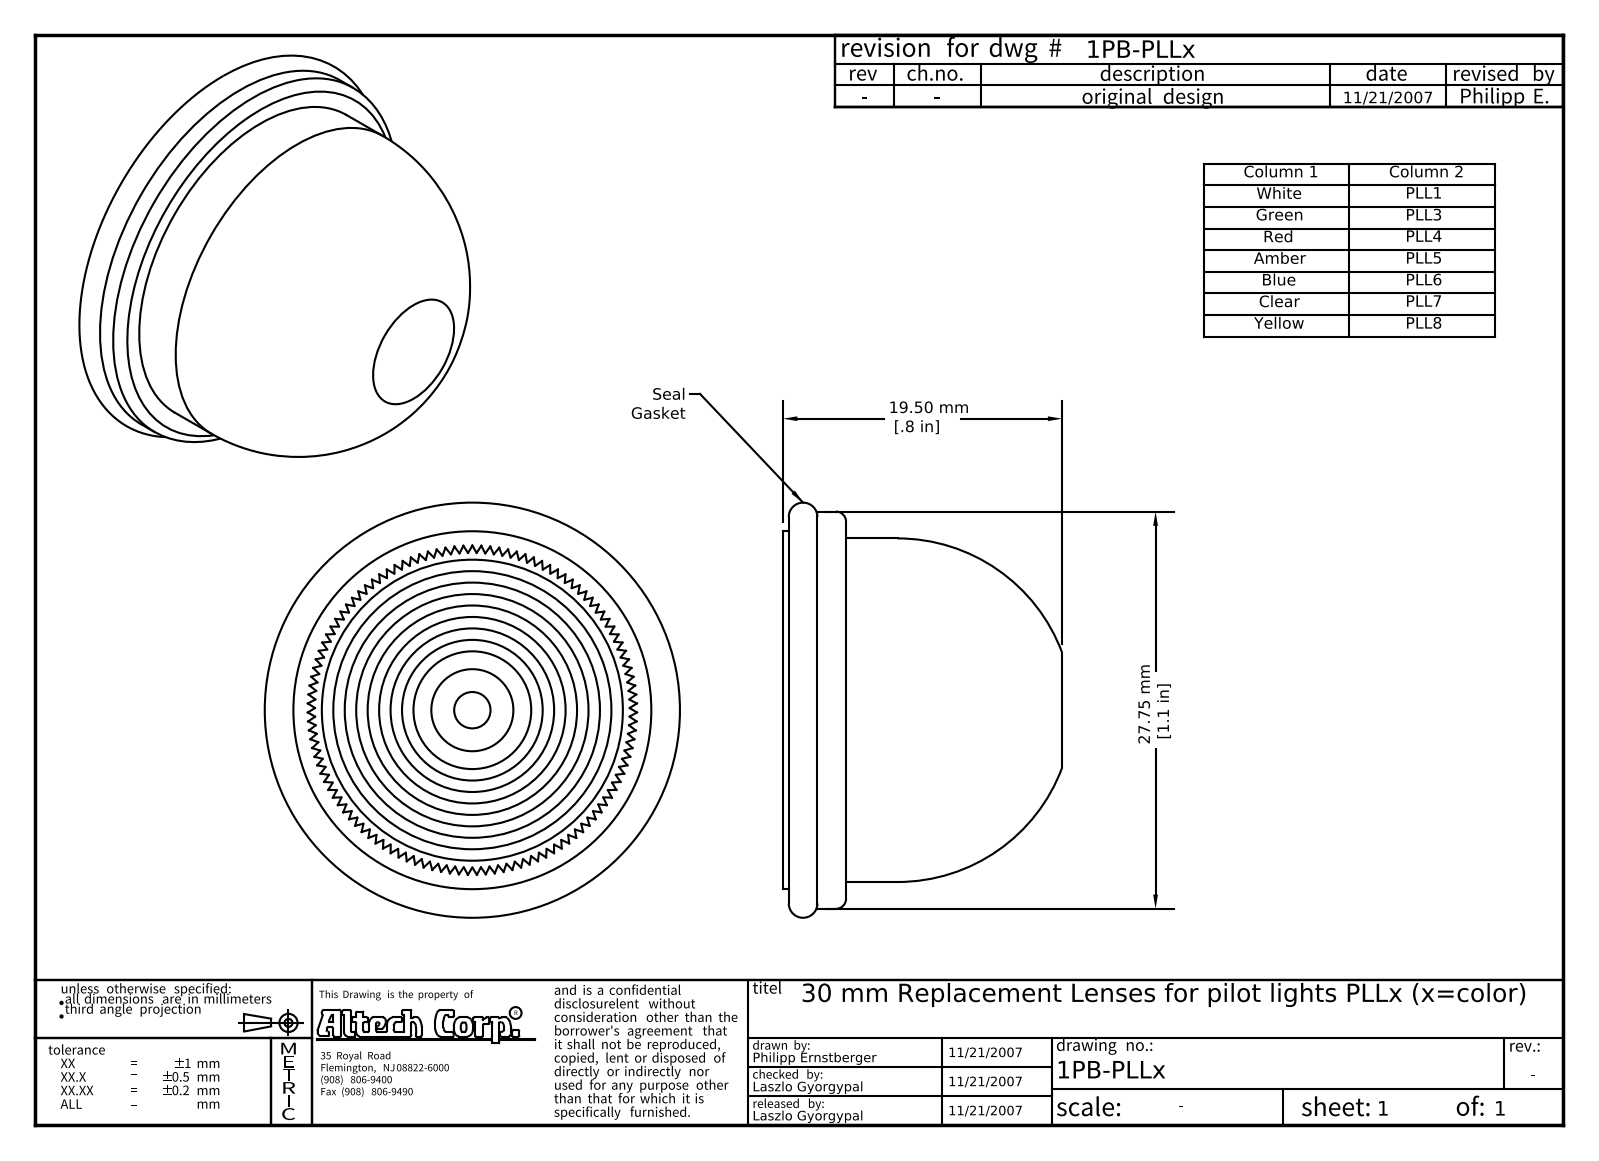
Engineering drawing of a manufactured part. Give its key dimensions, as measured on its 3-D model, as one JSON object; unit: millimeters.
{"part_name": "PLLx; cap; gasket", "step_written_by": "Autodesk Inventor 2008 (AUTOMOTIVE_DESIGN)", "units": "millimeters", "bodies": {"solids": 2, "faces": 378, "planar": 246, "cylindrical": 129, "other": 3}, "overall_size": [29, 29, 19.5], "volume_mm3": 1950, "surface_area_mm2": 4625, "round_holes": [[2.54, 1], [5.73, 1], [8.23, 1], [9.83, 1], [11.43, 1], [13.03, 1], [14.63, 1], [16.23, 1], [17.83, 1], [19.43, 1], [21.03, 1]], "round_bosses_or_shafts": [[27.75, 1], [25, 1], [24, 1]], "partial_cylinders_radius": [[11, 1]], "face_to_face_distances": [2, 3.8, 7.57, 2.4, 4.4, 11.37, 5, 3, 11.97, 9.57]}
